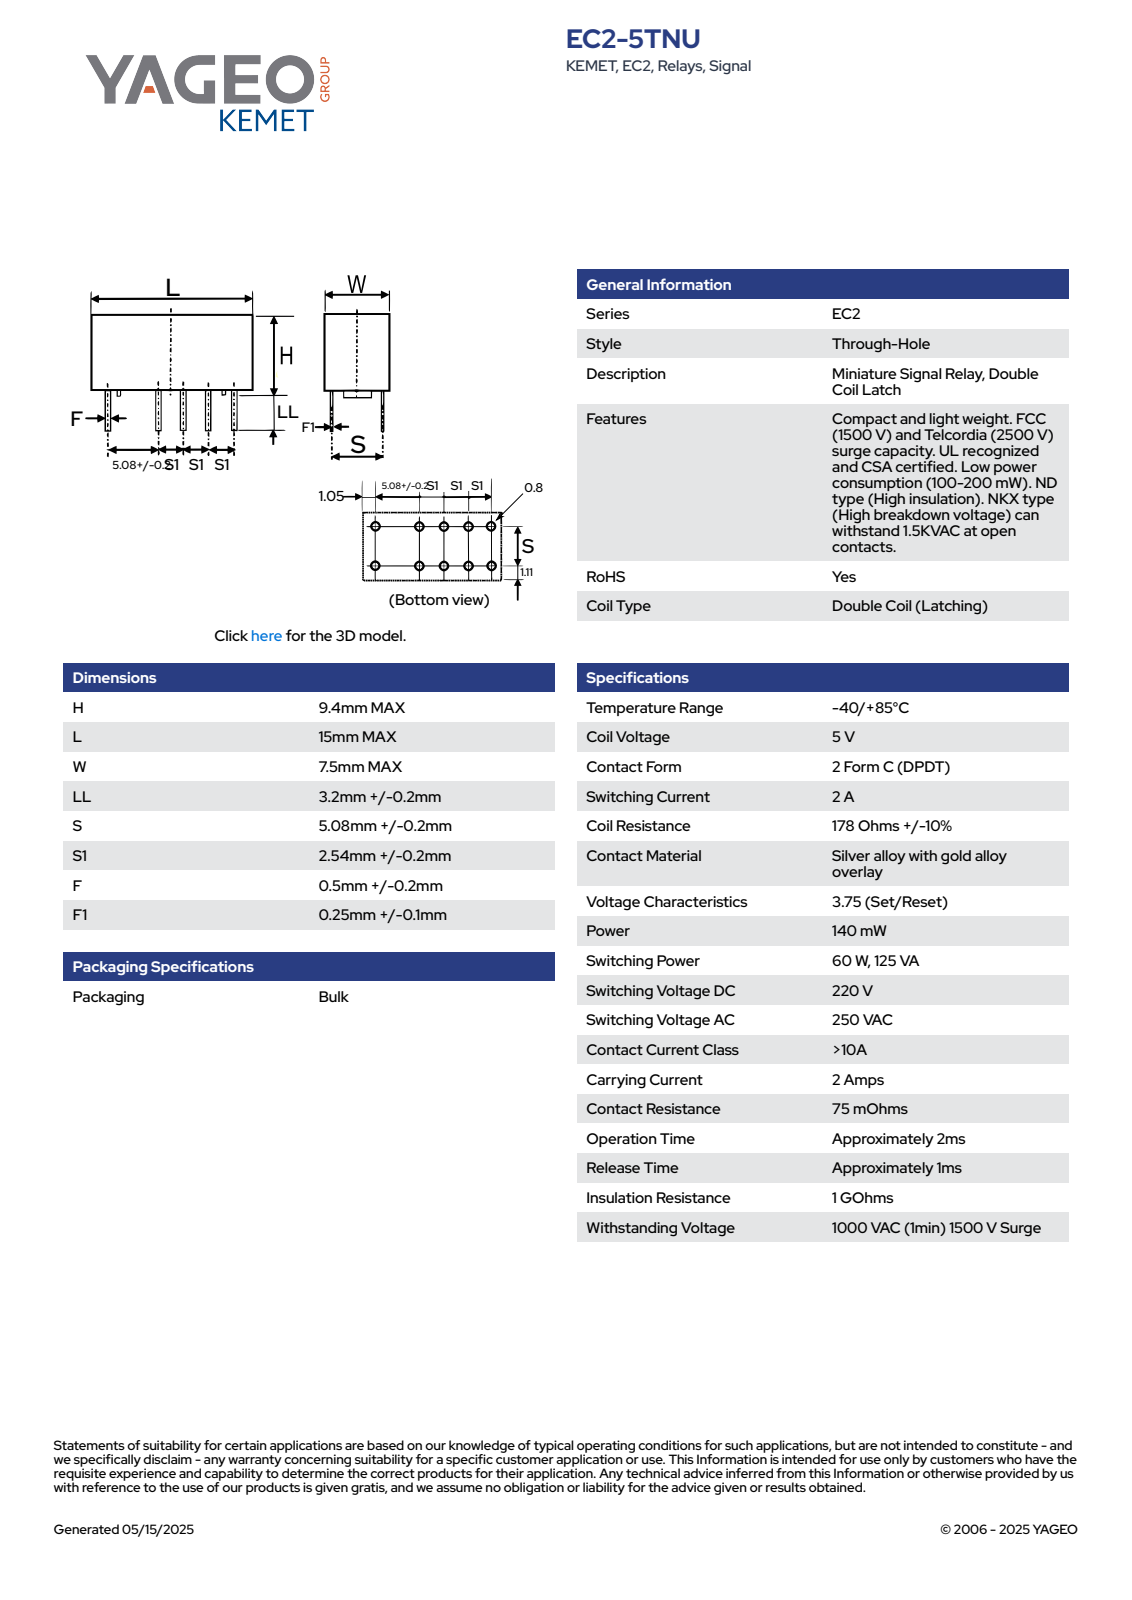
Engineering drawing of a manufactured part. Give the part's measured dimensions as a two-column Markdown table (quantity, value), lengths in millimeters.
| quantity | value |
| --- | --- |
| part name | IR_TEC2D_L15W7.5H9.4 |
| STEP written by | SolidWorks 2014 (AUTOMOTIVE_DESIGN) |
| units | millimeters |
| bodies | 1 solid, 110 faces (110 planar, 0 cylindrical, 0 other) |
| overall size | 15 × 12.8 × 7.5 |
| volume | 1 006 mm³ |
| surface area | 680 mm² |
| main face-to-face distances | 7.5, 8.9, 15, 5.08, 6.42, 0.5, 1.08, 1.33, 6.17, 2.54 |
